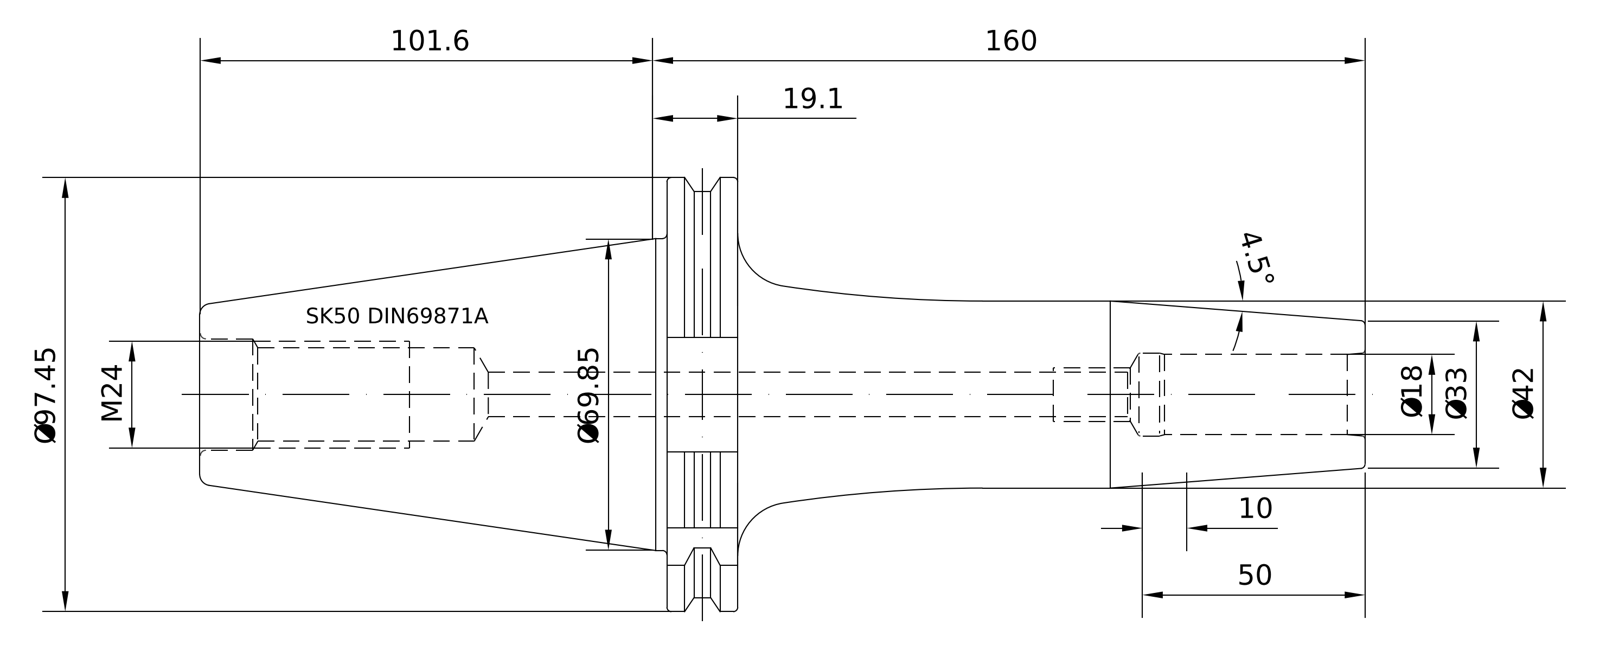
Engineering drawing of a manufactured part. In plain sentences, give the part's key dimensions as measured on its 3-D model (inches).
The part is named "50-442-18". Its 3-D file was written by "PRO/ENGINEER BY PARAMETRIC TECHNOLOGY CORPORATION, 2010430 (CONFIG_CONTROL_DESIGN)". It is 1 solid with 95 faces: 21 planar, 24 cylindrical and 50 other. Overall it measures 10.299 by 3.837 by 3.701 inches. Its volume is 31.91 cubic inches and its surface area 96.22 square inches. Round holes: 1 of diameter 0.709, 1 of diameter 0.817, 1 of diameter 0.985, 1 of diameter 1.012. Round bosses or shafts: 1 of diameter 3.583, 1 of diameter 2.722, 1 of diameter 1.654, 1 of diameter 0.945. Partial cylindrical surfaces (rounded edges, fillets, slot ends): 1 of radius 0.069, 1 of radius 1.919. The main face-to-face distances are 0.624, 6.173, 5.549, 2.866, 4.126, 4.75, 10.299, 1.016, 8.331, 4.205.
